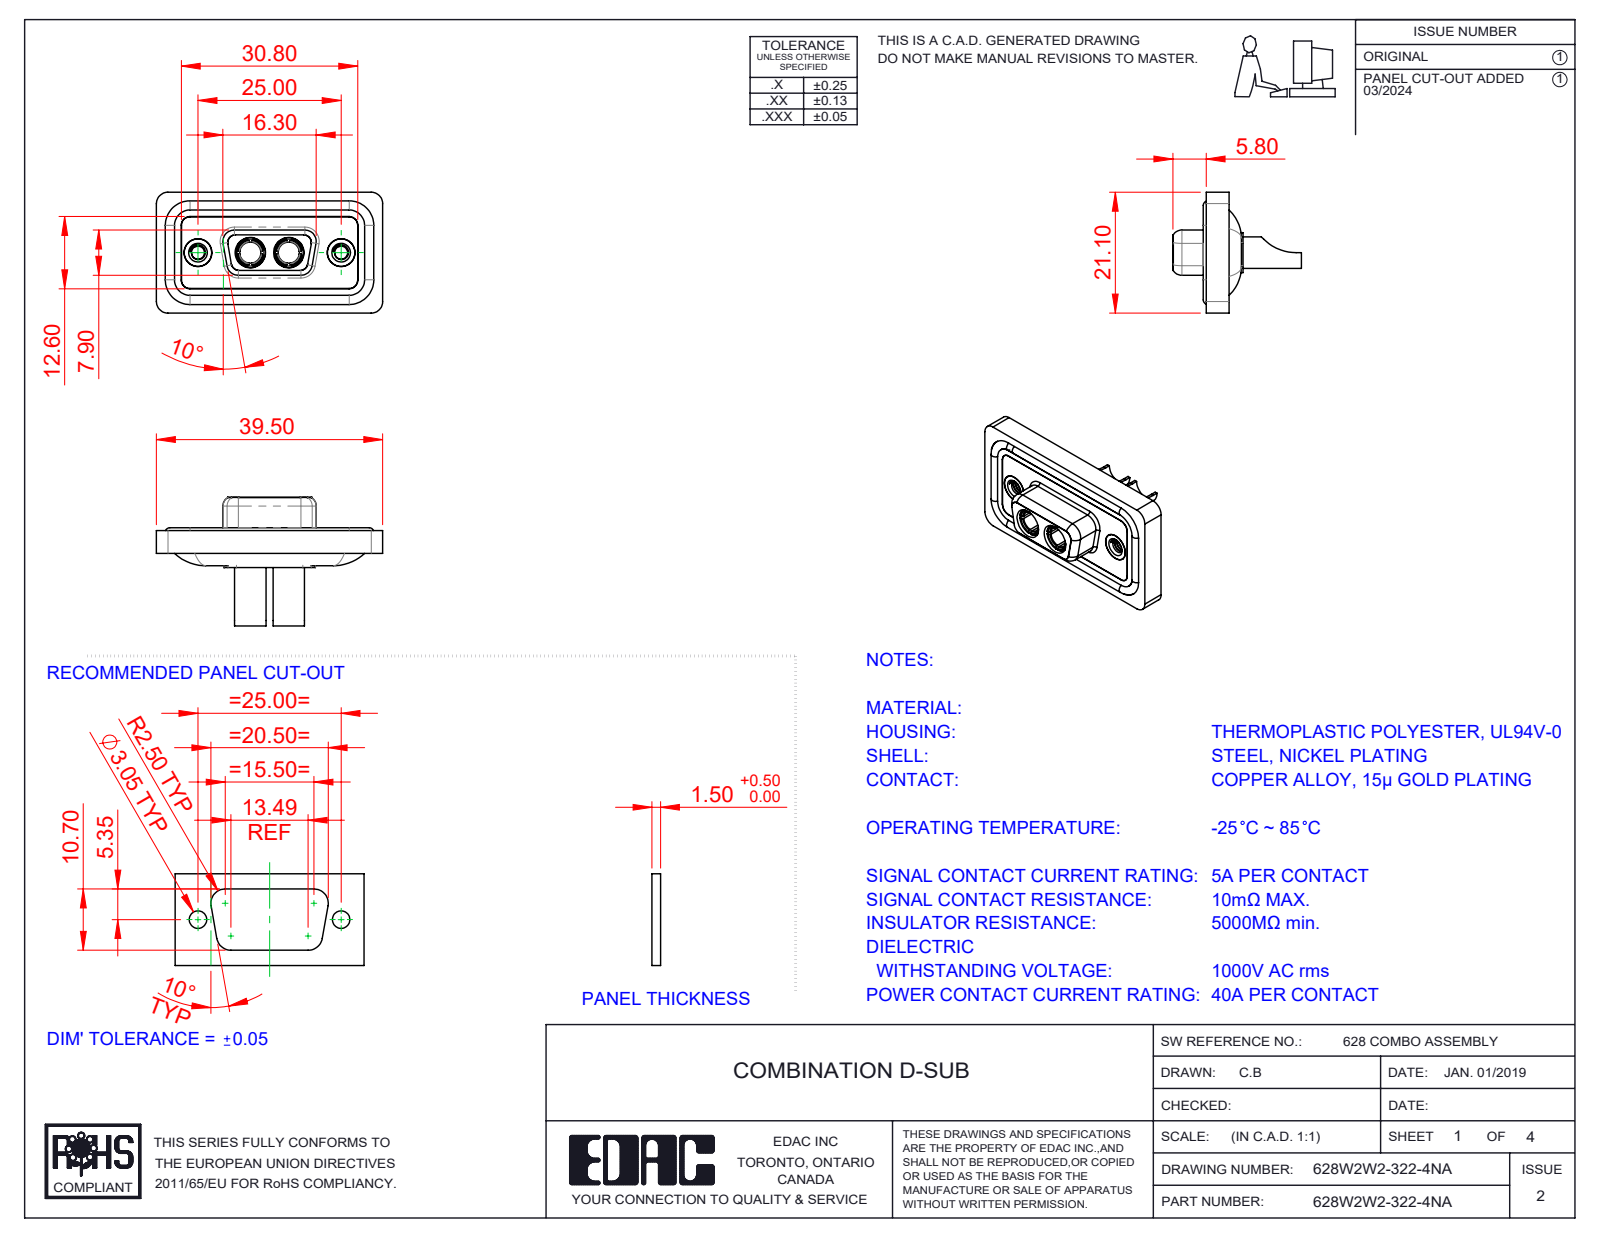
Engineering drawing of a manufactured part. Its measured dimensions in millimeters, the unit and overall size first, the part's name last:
Units: millimetres
Overall size (bounding box): 39.5 × 22.45 × 21.1
Round holes (diameter × count): ⌀4.85 ×4, ⌀2.26 ×2, ⌀3.7 ×2, ⌀4 ×2, ⌀4.05 ×2, ⌀4.6 ×2, ⌀5 ×2, ⌀5.3 ×2
Round bosses / shafts (diameter × count): ⌀1.6 ×4, ⌀5.5 ×2, ⌀5.2 ×2, ⌀4.96 ×2, ⌀4.95 ×2, ⌀4.8 ×2, ⌀4.75 ×2, ⌀3.75 ×2
Partial cylindrical surfaces — rounded edges, fillets, slot ends (radius × count): R1.5 ×22, R2 ×18, R1.35 ×8, R1.6 ×8, R0.25 ×4, R0.5 ×4, R0.6 ×4, R0.65 ×4
Main face-to-face distances: 0.4, 1.1, 2.9, 1.8, 0.5, 1.6, 5.65, 7.45, 5.35, 3.1
Hole centre spacings: 9.14, 15.86, 6.72, 25
Volume: 4 794 mm³ · Surface area: 7 913 mm²
Bodies: 11 solids, 538 faces (167 planar, 238 cylindrical, 133 other)
Part name (STEP PRODUCT): 628Combo Housing_2W2; 628Combo Shell Rear_09 Contacts; 628Combo Shell Front_09 Contacts; 628Combo Threaded Rivet_A (+3 more)
STEP written by: SolidWorks 2023 (CONFIG_CONTROL_DESIGN)
